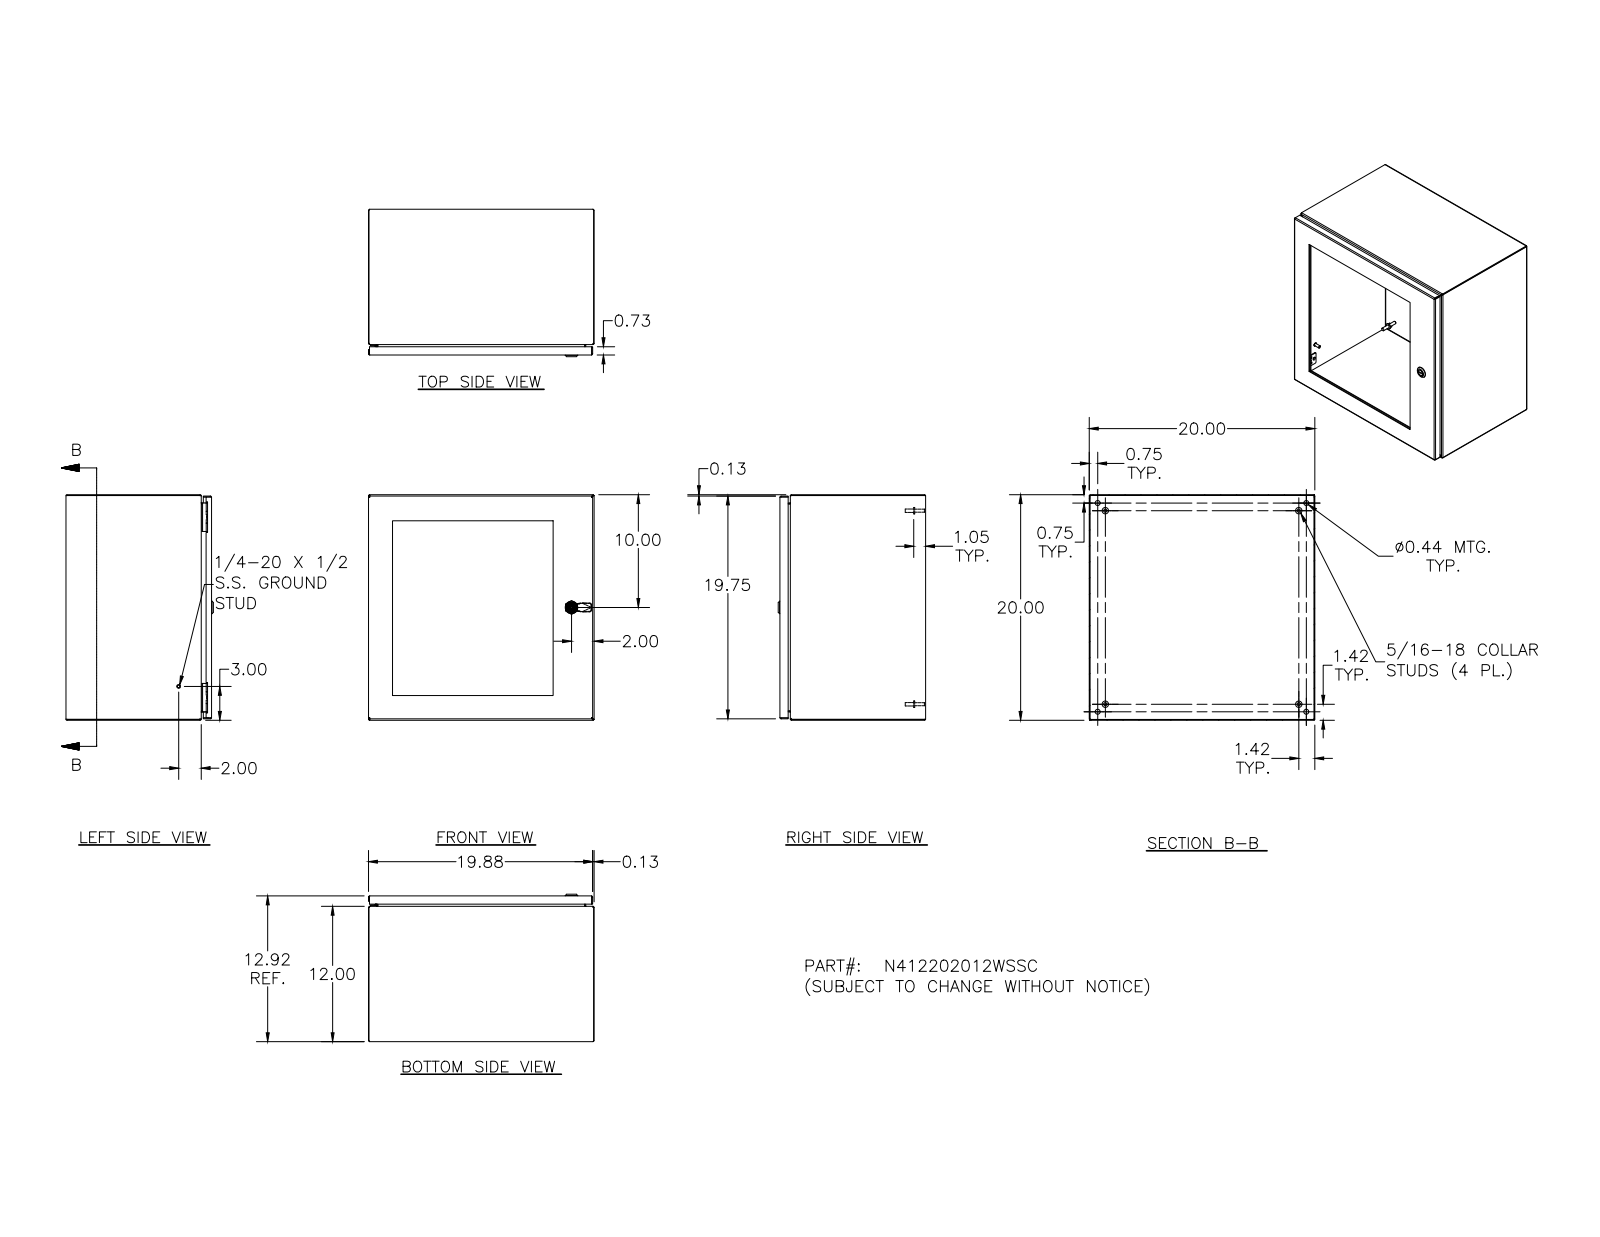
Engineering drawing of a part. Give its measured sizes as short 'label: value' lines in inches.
name: N412202012WSSC; N412202012WSSCBKP; N4122020WSSCLID; HFW328176 (+8 more)
written by: Autodesk Inventor 2011 (AUTOMOTIVE_DESIGN)
unit: in
bodies: 70 solids, 1940 faces (754 planar, 565 cylindrical, 621 other)
size: 20 × 20 × 13.075
volume: 194.1 in³; area: 4 103 in²
holes: 18× ⌀0.156, 16× ⌀0.281, 4× ⌀0.093, 4× ⌀0.152, 4× ⌀0.167, 4× ⌀0.172, 4× ⌀0.188, 4× ⌀0.437, 1× ⌀0.187, 1× ⌀0.197, 1× ⌀0.315, 1× ⌀0.394
bosses: 16× ⌀0.19, 15× ⌀0.253, 10× ⌀0.25, 4× ⌀0.563, 4× ⌀0.36, 4× ⌀0.32, 4× ⌀0.3, 4× ⌀0.275
rounds: 34× R0.031, 26× R0.05, 24× R0.105, 18× R0.016, 16× R0.125, 9× R0.02, 8× R0.032, 4× R0.157
face distances: 0.074, 19.926, 12.843, 20, 19.852, 12.769, 0.25, 12.593, 12.519, 12.917
hole spacings: 4, 8, 16.008, 16, 17.221, 6.221, 8.585, 10.035
